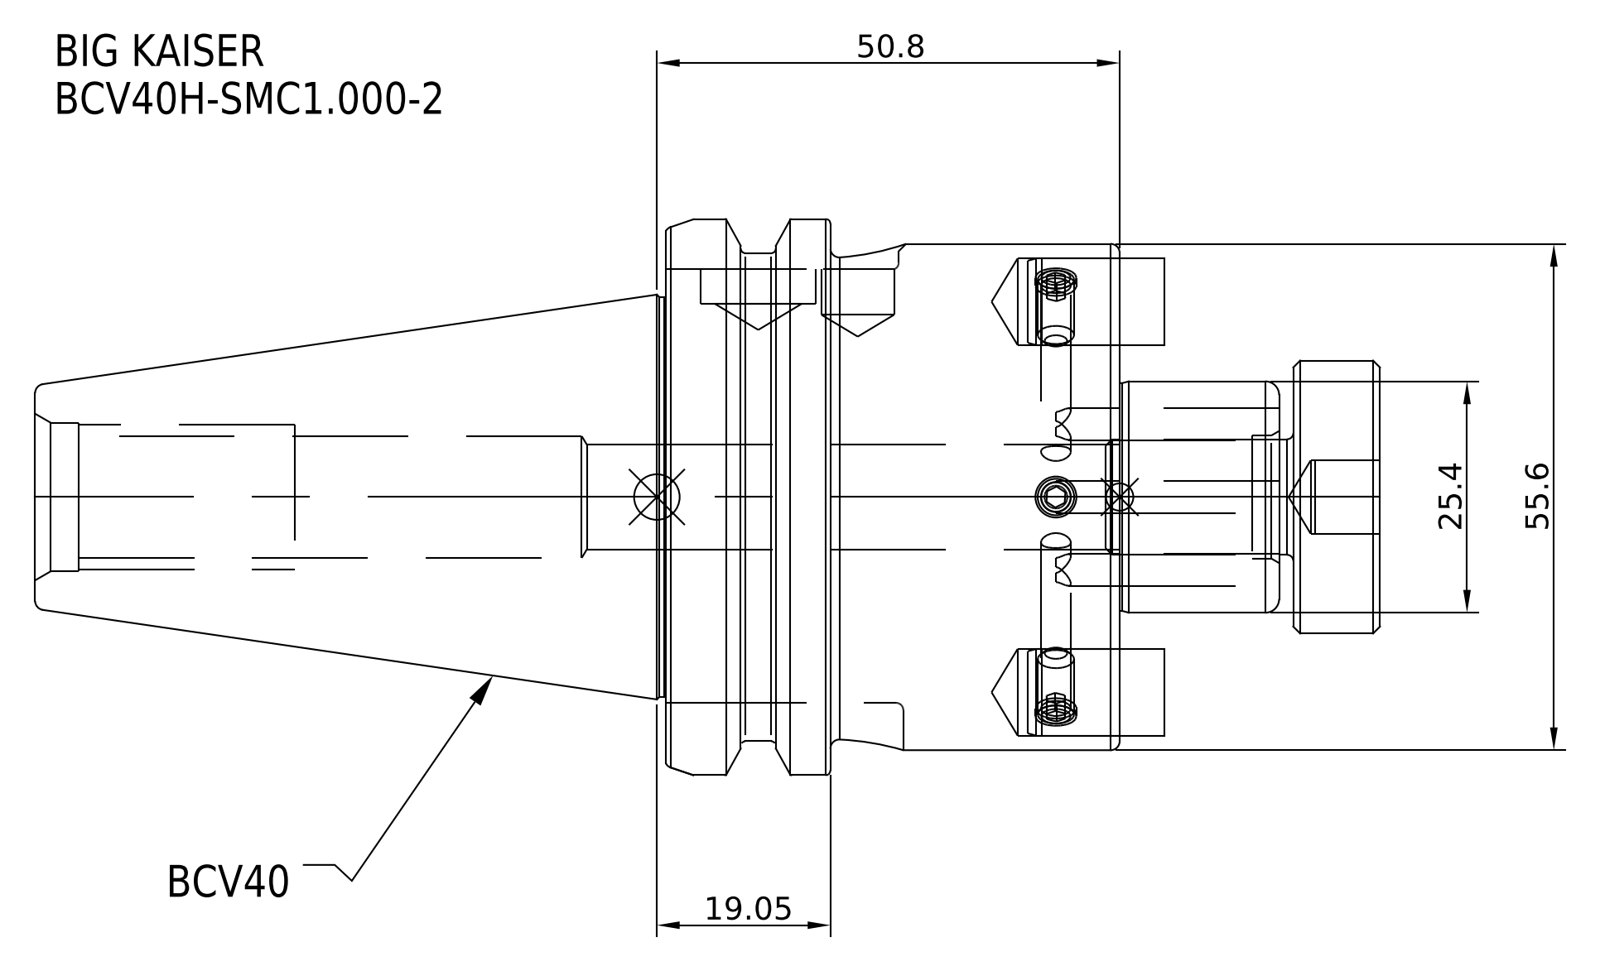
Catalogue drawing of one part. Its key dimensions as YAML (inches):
part_name: "BCV40H-SMC1_000-2"
step_written_by: "SolidWorks 2021 (CONFIG_CONTROL_DESIGN)"
units: inches
bodies: {solids: 1, faces: 38, planar: 18, cylindrical: 14, other: 6}
overall_size: [4.939, 2.752, 2.752]
volume: 12.94
surface_area: 42.21
round_holes:
  - {diameter: 0.578, count: 1}
round_bosses_or_shafts:
  - {diameter: 2.752, count: 1}
  - {diameter: 2.5, count: 1}
  - {diameter: 2.219, count: 1}
  - {diameter: 2.189, count: 1}
  - {diameter: 1.75, count: 1}
face_to_face_distances: [1.961, 0.346, 1.614, 1.25, 0.904, 0.711, 0.252, 0.598, 1.502, 2.213]
